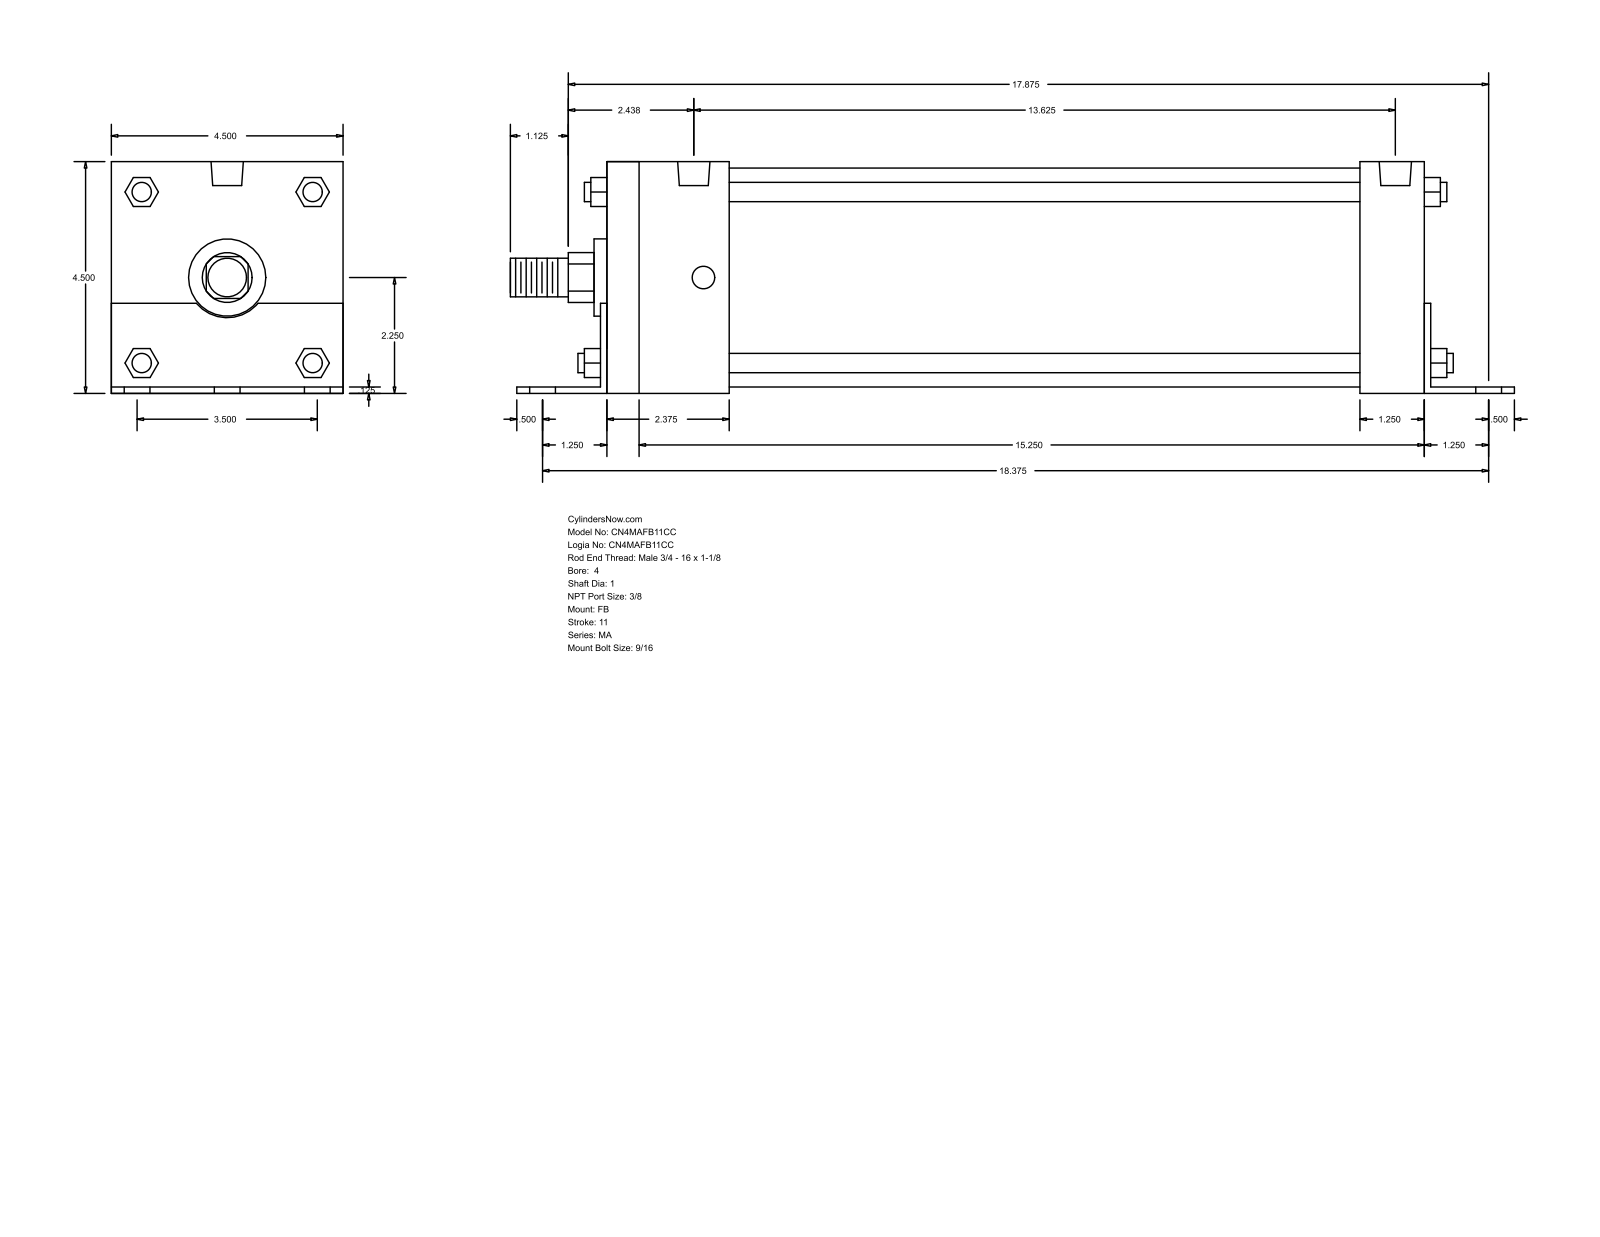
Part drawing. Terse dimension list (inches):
name: MA_FB__0400_1
written by: GSSL Pune (CONFIG_CONTROL_DESIGN)
unit: in
bodies: 0 solids, 140 faces (105 planar, 35 cylindrical, 0 other)
size: 19.5 × 4.502 × 4.5
holes: 6× ⌀0.563, 4× ⌀0.437, 2× ⌀0.627
bosses: 4× ⌀0.375, 1× ⌀4.25, 1× ⌀1.5, 1× ⌀1, 1× ⌀0.75
rounds: 1× R0.484, 1× R0.78
face distances: 4.5, 0.125, 4.502, 0.123, 4.377, 15.875, 0.125, 16.125, 16, 16
hole spacings: 1.75, 18.458, 18.375, 0.187, 2.519, 2.657, 3.419, 3.5
